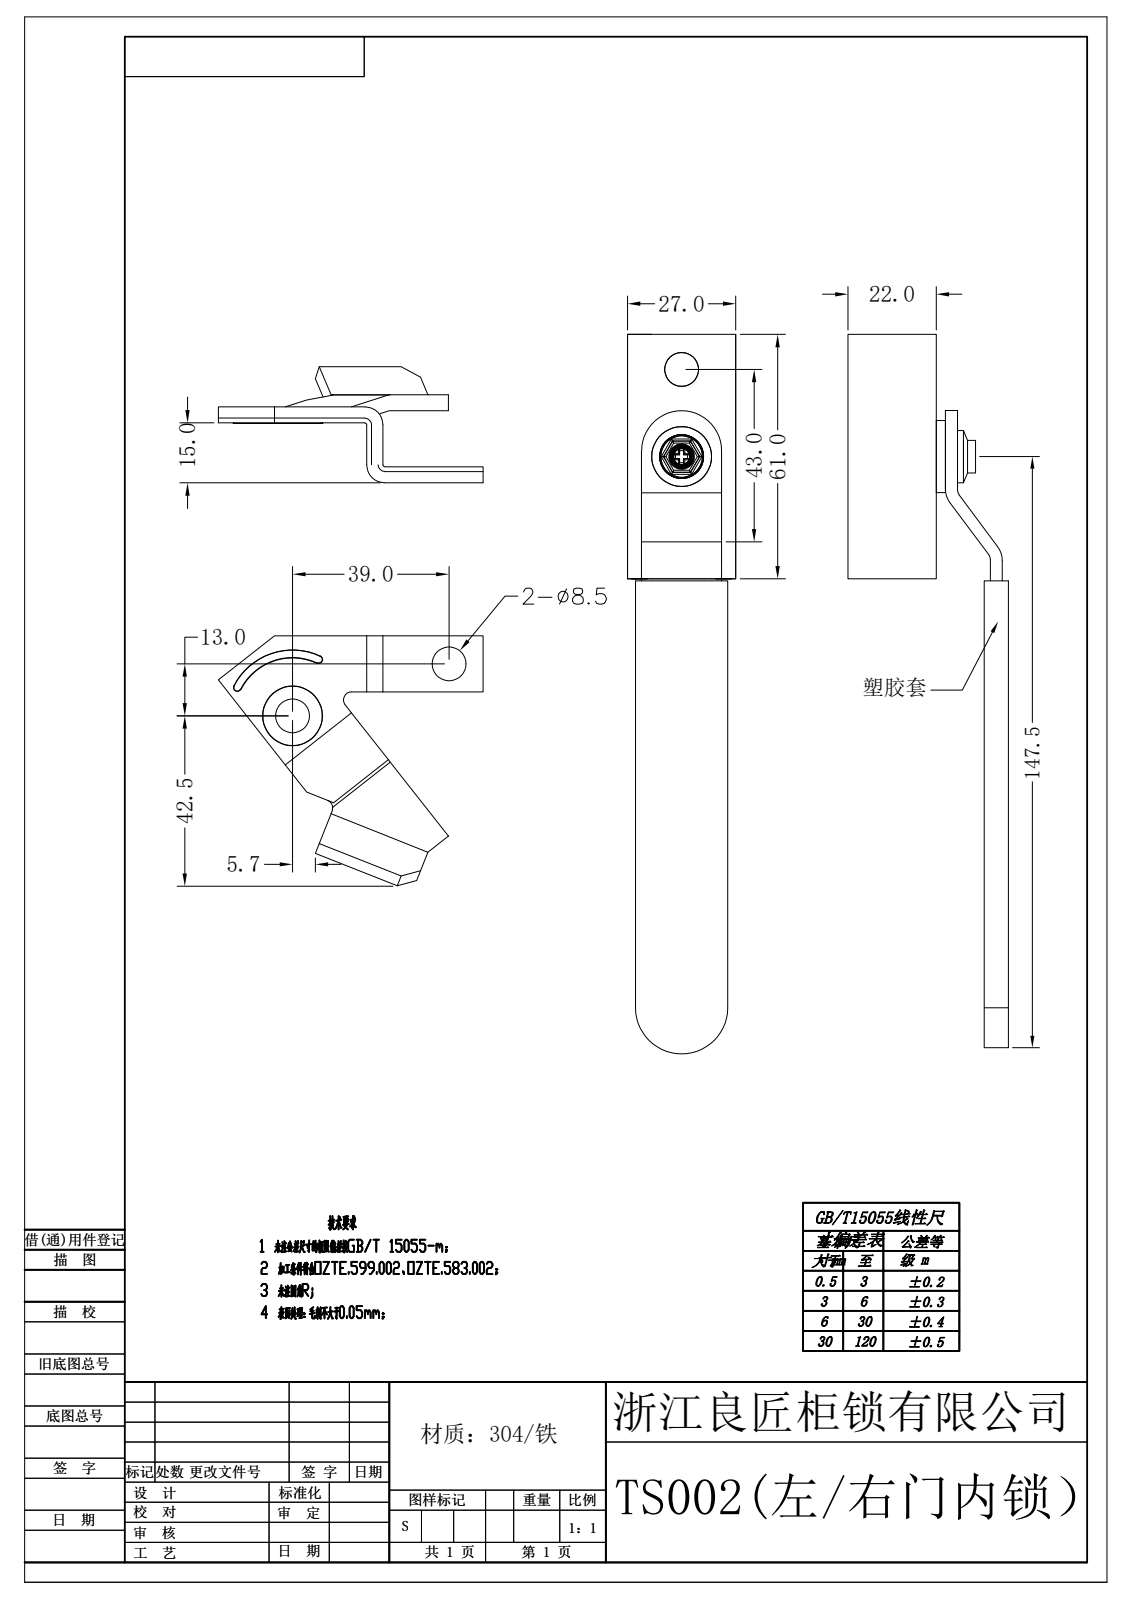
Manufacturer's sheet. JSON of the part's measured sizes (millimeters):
{"step_written_by": "Rhino 8.5 (CONFIG_CONTROL_DESIGN)", "units": "millimeters", "bodies": {"solids": 6, "faces": 330, "planar": 161, "cylindrical": 135, "other": 34}, "overall_size": [305.21, 178, 67.68], "volume_mm3": 51886, "surface_area_mm2": 35880, "round_holes": [[8.5, 6], [15, 2], [2.87, 1], [11, 1]], "round_bosses_or_shafts": [[18, 1], [15, 1], [13, 1]], "partial_cylinders_radius": [[0.3, 20], [0.5, 4], [1.53, 4], [2, 4], [4.5, 4], [4, 2], [6, 2], [7.61, 1]], "face_to_face_distances": [4, 6, 1, 5, 20, 19, 21, 25, 15, 3], "hole_center_spacings": [21.75, 41.11, 105.71, 43.5, 65.91, 139.42, 140.28, 143.91]}
